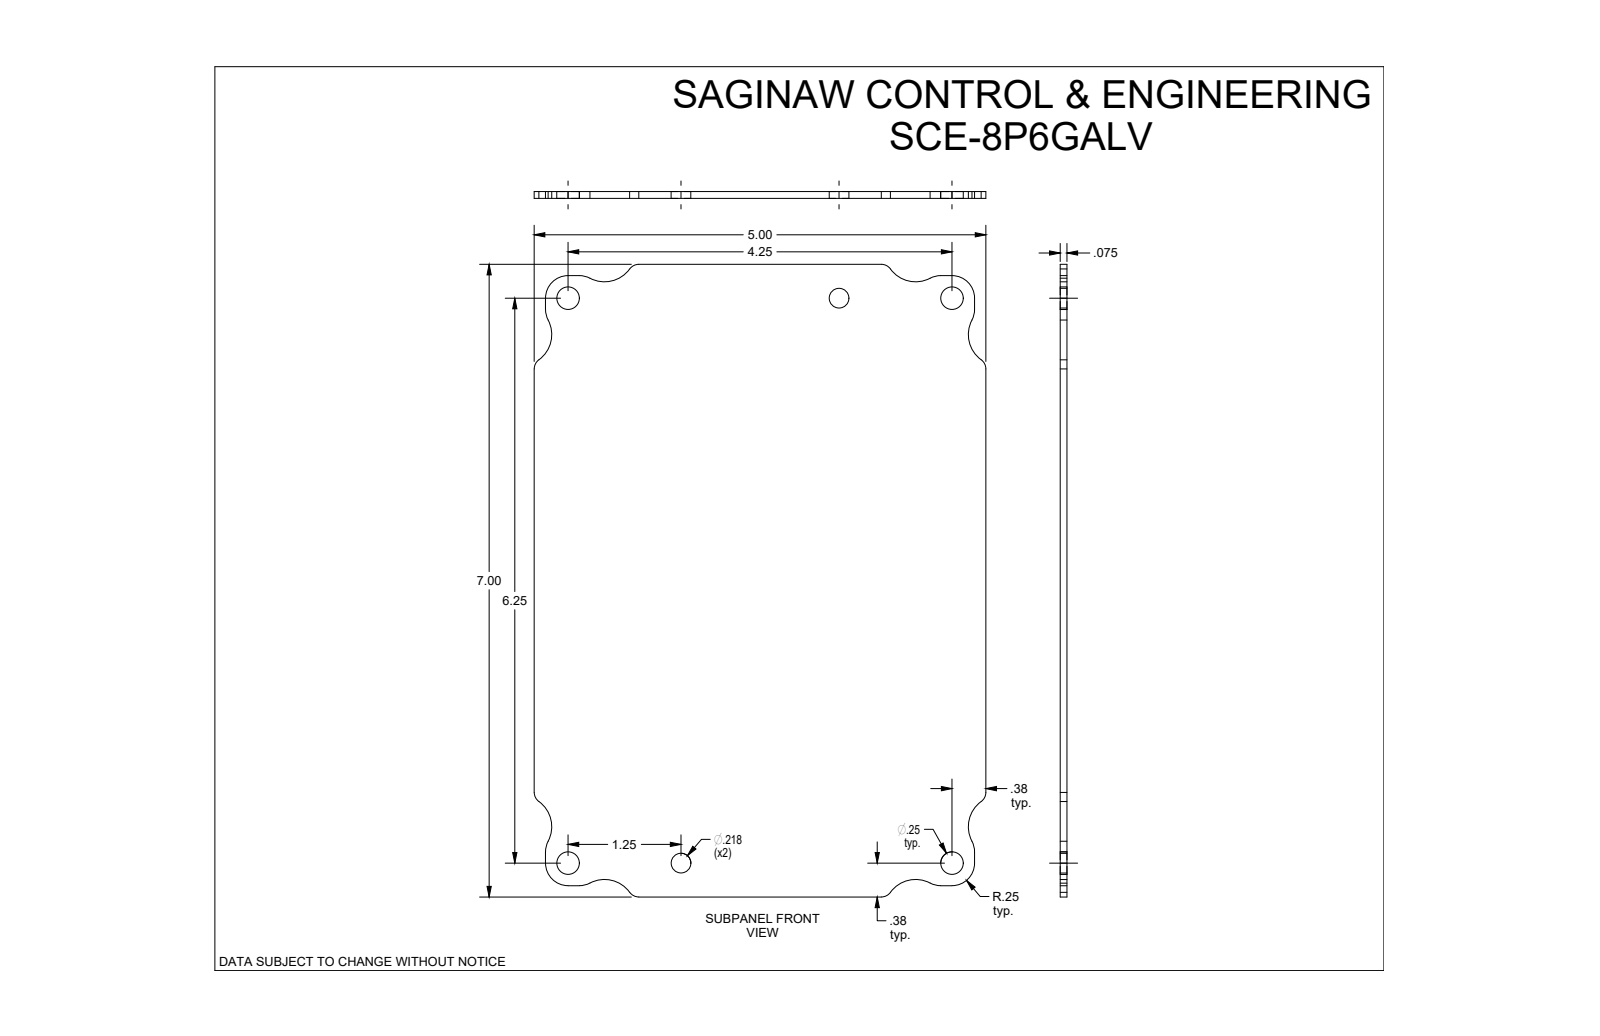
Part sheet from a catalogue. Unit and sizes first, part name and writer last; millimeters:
Units: millimetres
Overall size (bounding box): 177.8 × 127 × 1.9
Round holes (diameter × count): ⌀6.4 ×4, ⌀5.5 ×2
Partial cylindrical surfaces — rounded edges, fillets, slot ends (radius × count): R6.4 ×12, R3.2 ×8, R8.7 ×8
Main face-to-face distances: 1.9, 127, 177.8, 3.2, 123.8, 174.6, 120.7, 171.5
Hole centre spacings: 31.8, 76.2, 108, 158.8, 161.9, 176.1, 192, 164.9
Volume: 41 210 mm³ · Surface area: 44 600 mm²
Bodies: 1 solid, 48 faces (14 planar, 34 cylindrical, 0 other)
Part name (STEP PRODUCT): SCE-8P6GALV
STEP written by: SolidWorks 2019 (CONFIG_CONTROL_DESIGN)
